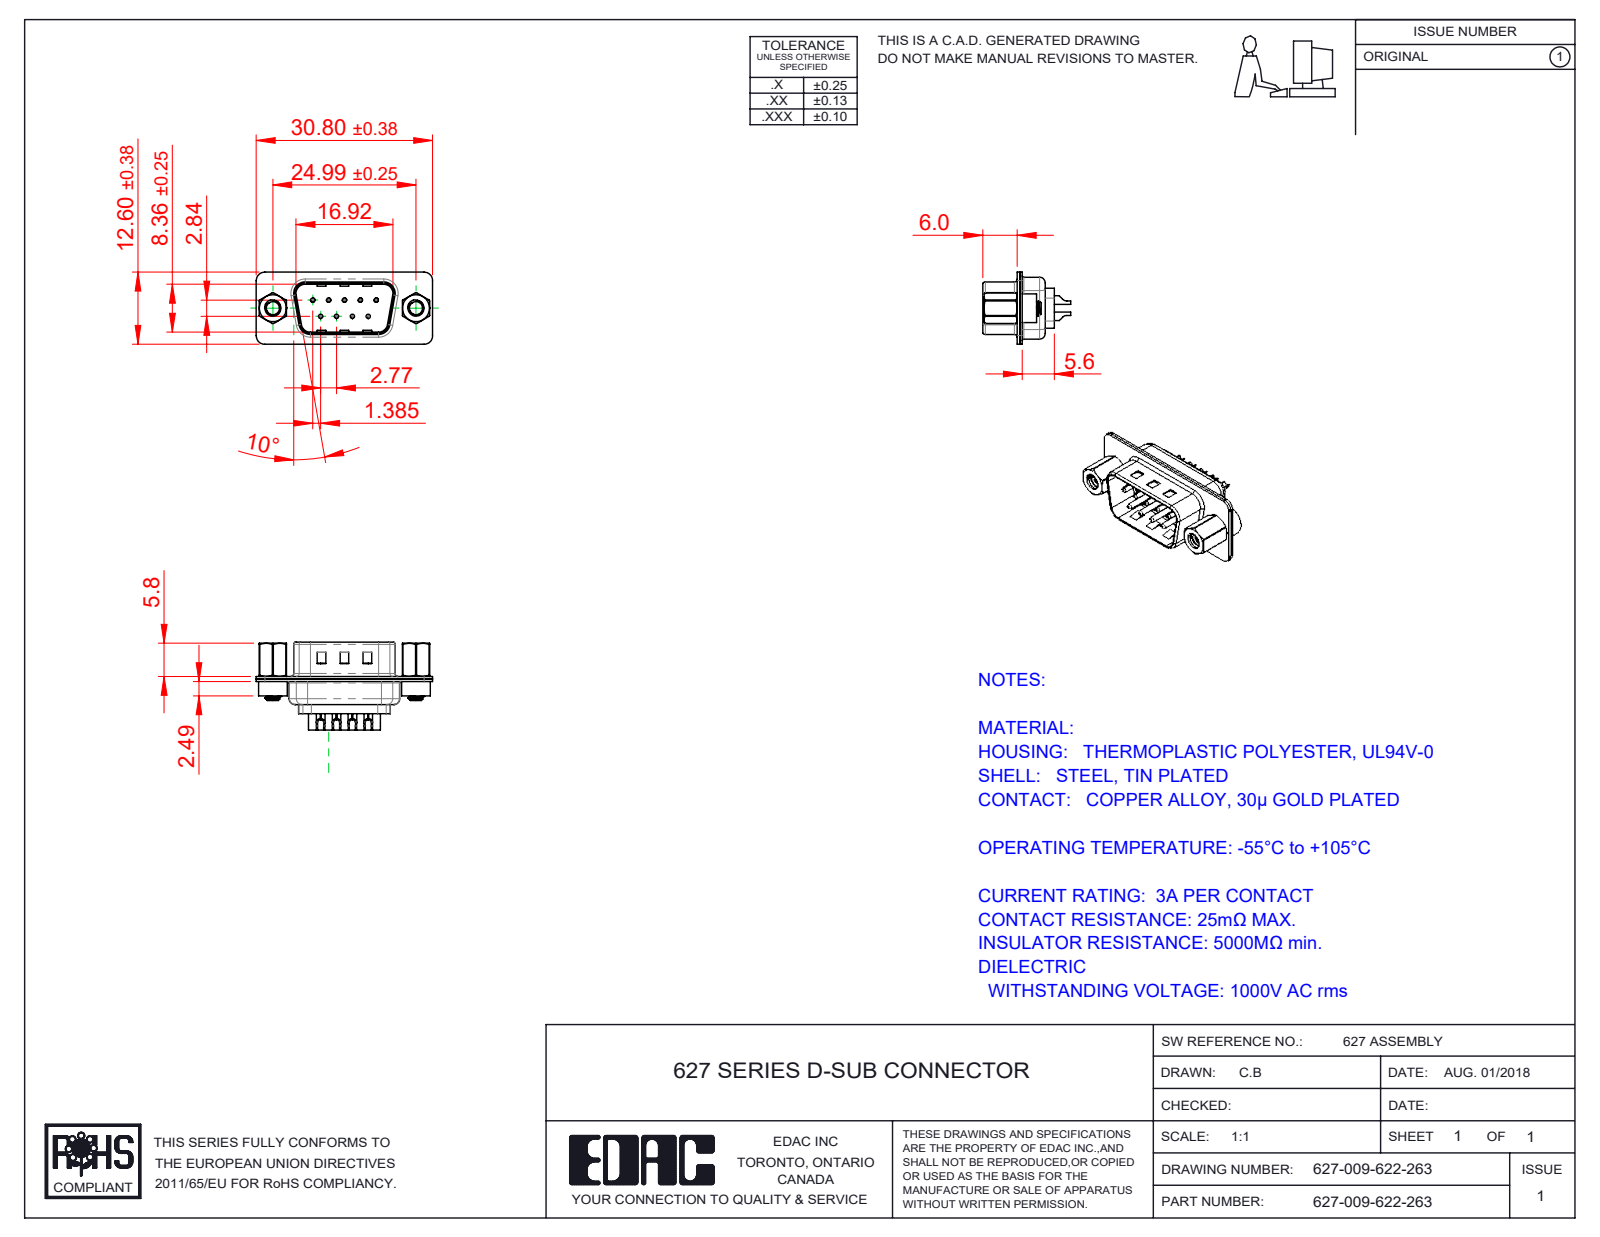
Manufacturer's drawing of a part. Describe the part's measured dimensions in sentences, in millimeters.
The part is named "627-009-622-263; 627 Shell Front_09 Contacts; 627 4-40 Threaded Rivet; 627 4-40 Hex Standoff (+4 more)". Its 3-D file was written by "SolidWorks 2020 (CONFIG_CONTROL_DESIGN)". It is 16 solids with 1002 faces: 255 planar, 460 cylindrical and 287 other. Overall it measures 30.8 by 15.35 by 12.6 millimeters. Its volume is 1 523 cubic millimeters and its surface area 4 425 square millimeters. Round holes: 9 of diameter 0.35, 9 of diameter 1.1, 9 of diameter 1.6, 2 of diameter 2.26, 2 of diameter 2.29, 2 of diameter 4, 2 of diameter 4.8. Round bosses or shafts: 9 of diameter 2, 9 of diameter 1.5, 9 of diameter 0.75, 2 of diameter 5, 2 of diameter 4.9, 2 of diameter 2.79. Partial cylindrical surfaces (rounded edges, fillets, slot ends): 18 of radius 1.5, 12 of radius 2, 8 of radius 0.5, 8 of radius 1.6, 6 of radius 1, 4 of radius 0.25, 4 of radius 0.6, 4 of radius 0.65. The main face-to-face distances are 0.45, 0.4, 0.9, 0.82, 9.58, 1.4, 8.76, 0.5, 1.5, 6.5. The hole center spacings are 3.16, 2.77, 5.54, 5.03, 5.04, 8.31, 7.48, 7.49.
